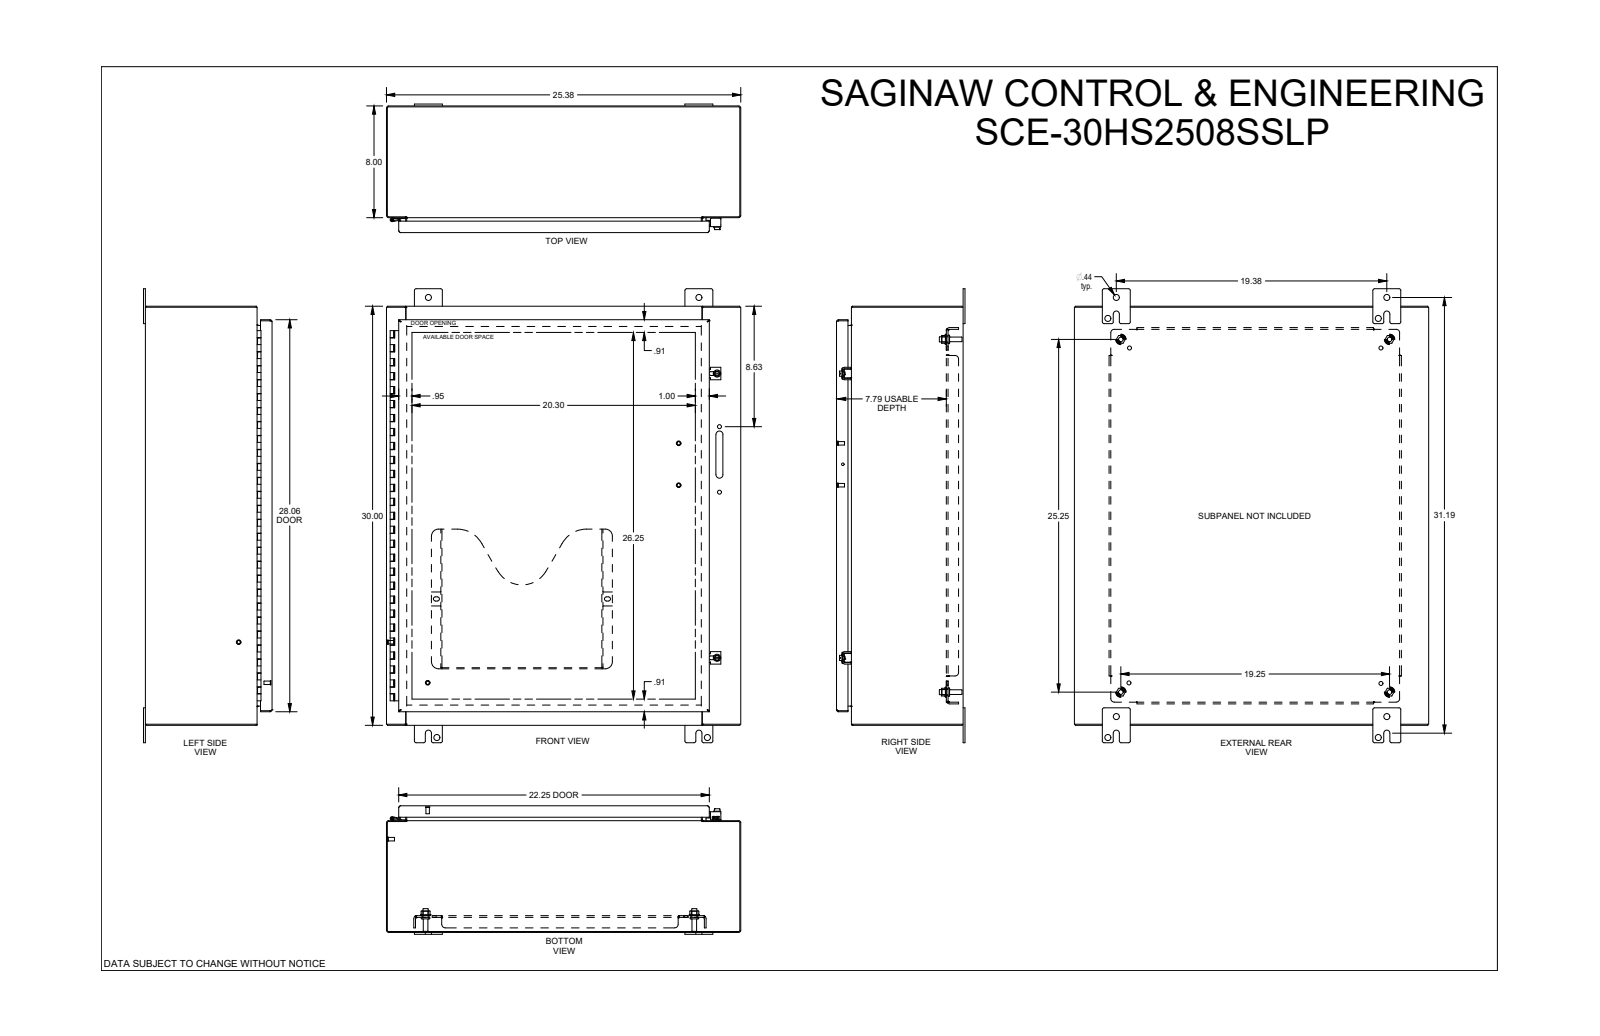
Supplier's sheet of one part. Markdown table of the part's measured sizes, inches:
| quantity | value |
| --- | --- |
| part name | SCE-30HS2508LP |
| STEP written by | SolidWorks 2021 (AUTOMOTIVE_DESIGN) |
| units | inches |
| bodies | 57 solids, 2668 faces (981 planar, 771 cylindrical, 916 other) |
| overall size | 32.5 × 25.375 × 9.343 |
| volume | 308.3 in³ |
| surface area | 7 062 in² |
| round holes (diameter × count) | 0.281 × 6, 0.312 × 6, 0.172 × 4, 0.205 × 4, 0.244 × 4, 0.31 × 4, 0.367 × 4, 0.375 × 4, 0.5 × 4, 0.04 × 2, 0.203 × 2, 0.218 × 2 |
| round bosses / shafts (diameter × count) | 0.248 × 8, 0.25 × 6, 0.17 × 6, 0.59 × 4, 0.376 × 4, 0.366 × 4, 0.332 × 4, 0.24 × 4 |
| partial cylindrical surfaces (radius × count) | 0.01 × 107, 0.025 × 72, 0.015 × 24, 0.185 × 21, 0.04 × 18, 0.029 × 12, 0.043 × 12, 0.118 × 12 |
| main face-to-face distances | 0.075, 8.993, 8.918, 1.125, 1.2, 7.868, 7.793, 9.068, 0.125, 1.075 |
| hole center spacings | 28.5, 0.875, 1.637, 2.282, 24.089, 24.582, 25.069, 26.259 |
